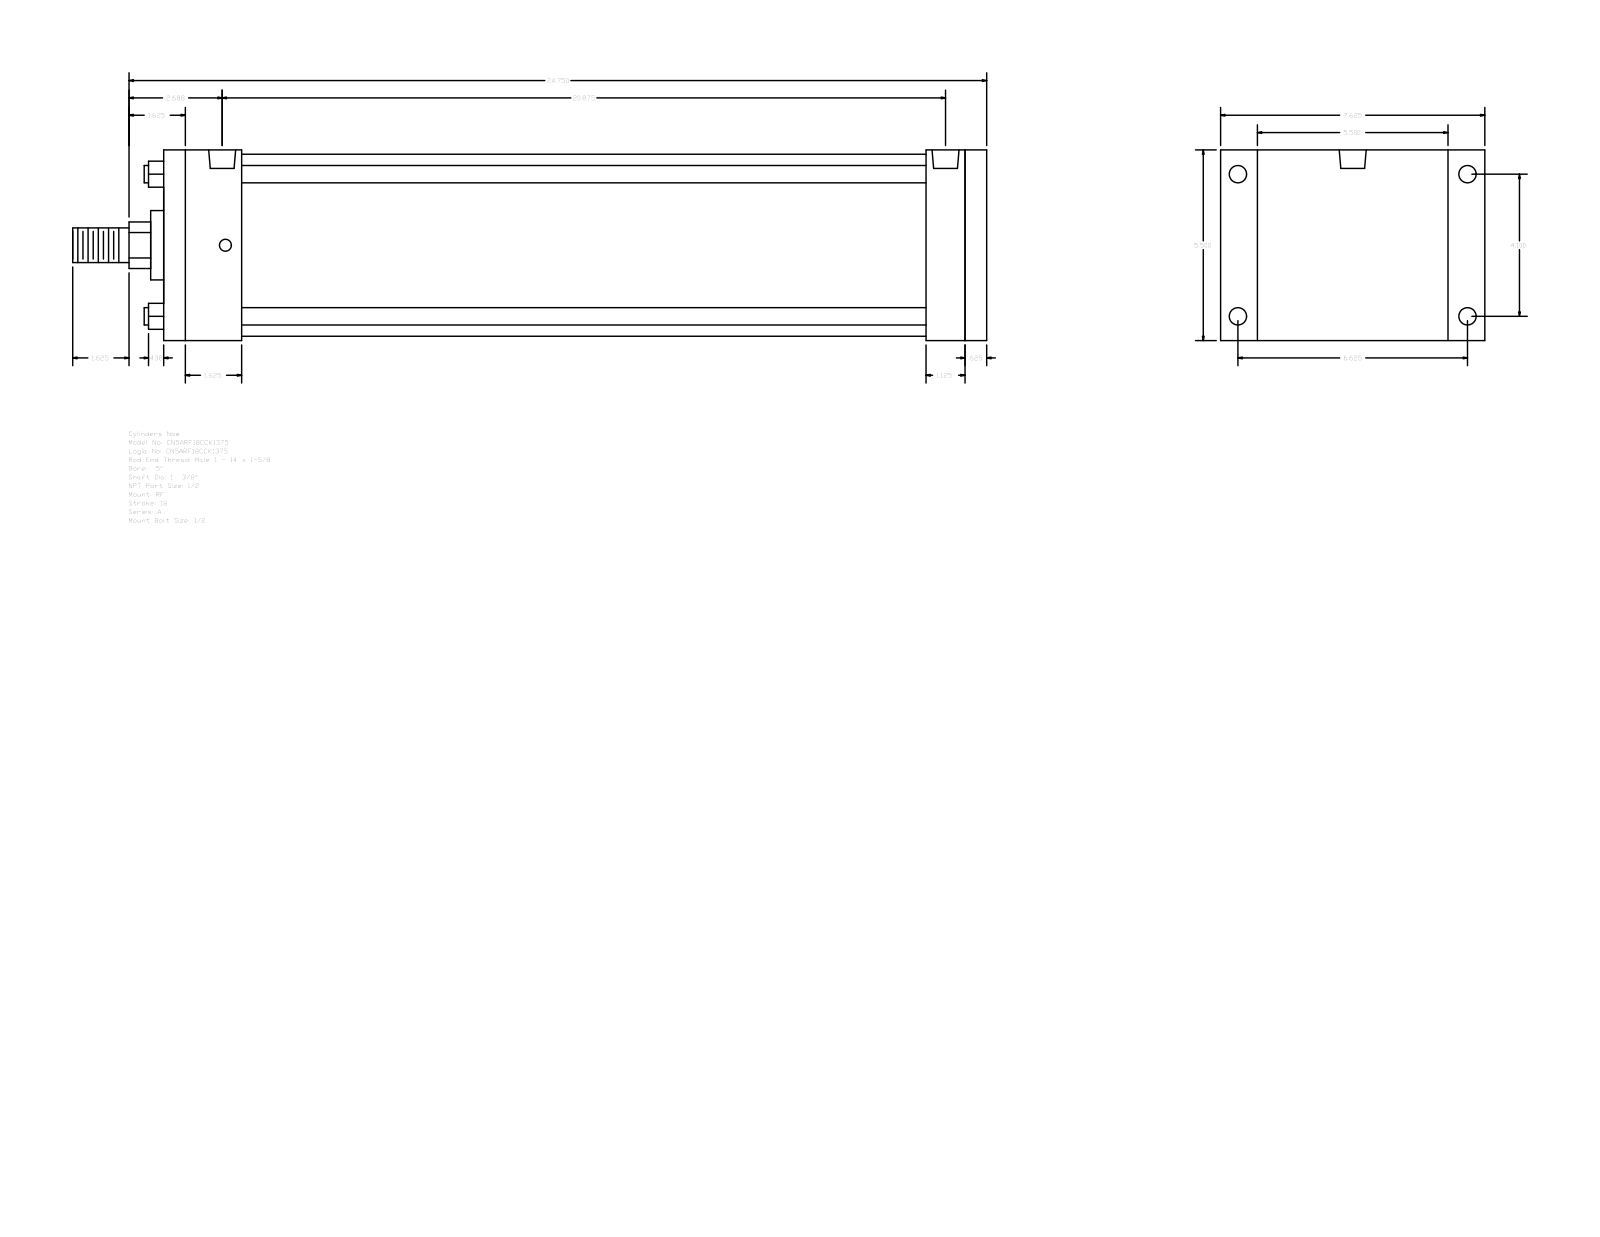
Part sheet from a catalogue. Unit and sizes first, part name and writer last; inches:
Units: inches
Overall size (bounding box): 26.375 × 7.625 × 5.5
Round holes (diameter × count): ⌀0.344 ×4, ⌀0.5 ×4, ⌀0.778 ×2
Round bosses / shafts (diameter × count): ⌀0.5 ×4, ⌀5.25 ×1, ⌀2 ×1, ⌀1.375 ×1, ⌀1 ×1
Partial cylindrical surfaces — rounded edges, fillets, slot ends (radius × count): R0.672 ×1
Main face-to-face distances: 5.5, 23.75, 0.625, 23.125, 2.25, 20.875, 21.5, 22, 19.75, 1.125
Hole centre spacings: 0.094, 4.1, 6.625, 7.791, 20.687, 20.781, 20.875
Bodies: 0 solids, 92 faces (64 planar, 28 cylindrical, 0 other)
Part name (STEP PRODUCT): A_RF__0500_1.375
STEP written by: GSSL Pune (CONFIG_CONTROL_DESIGN)
